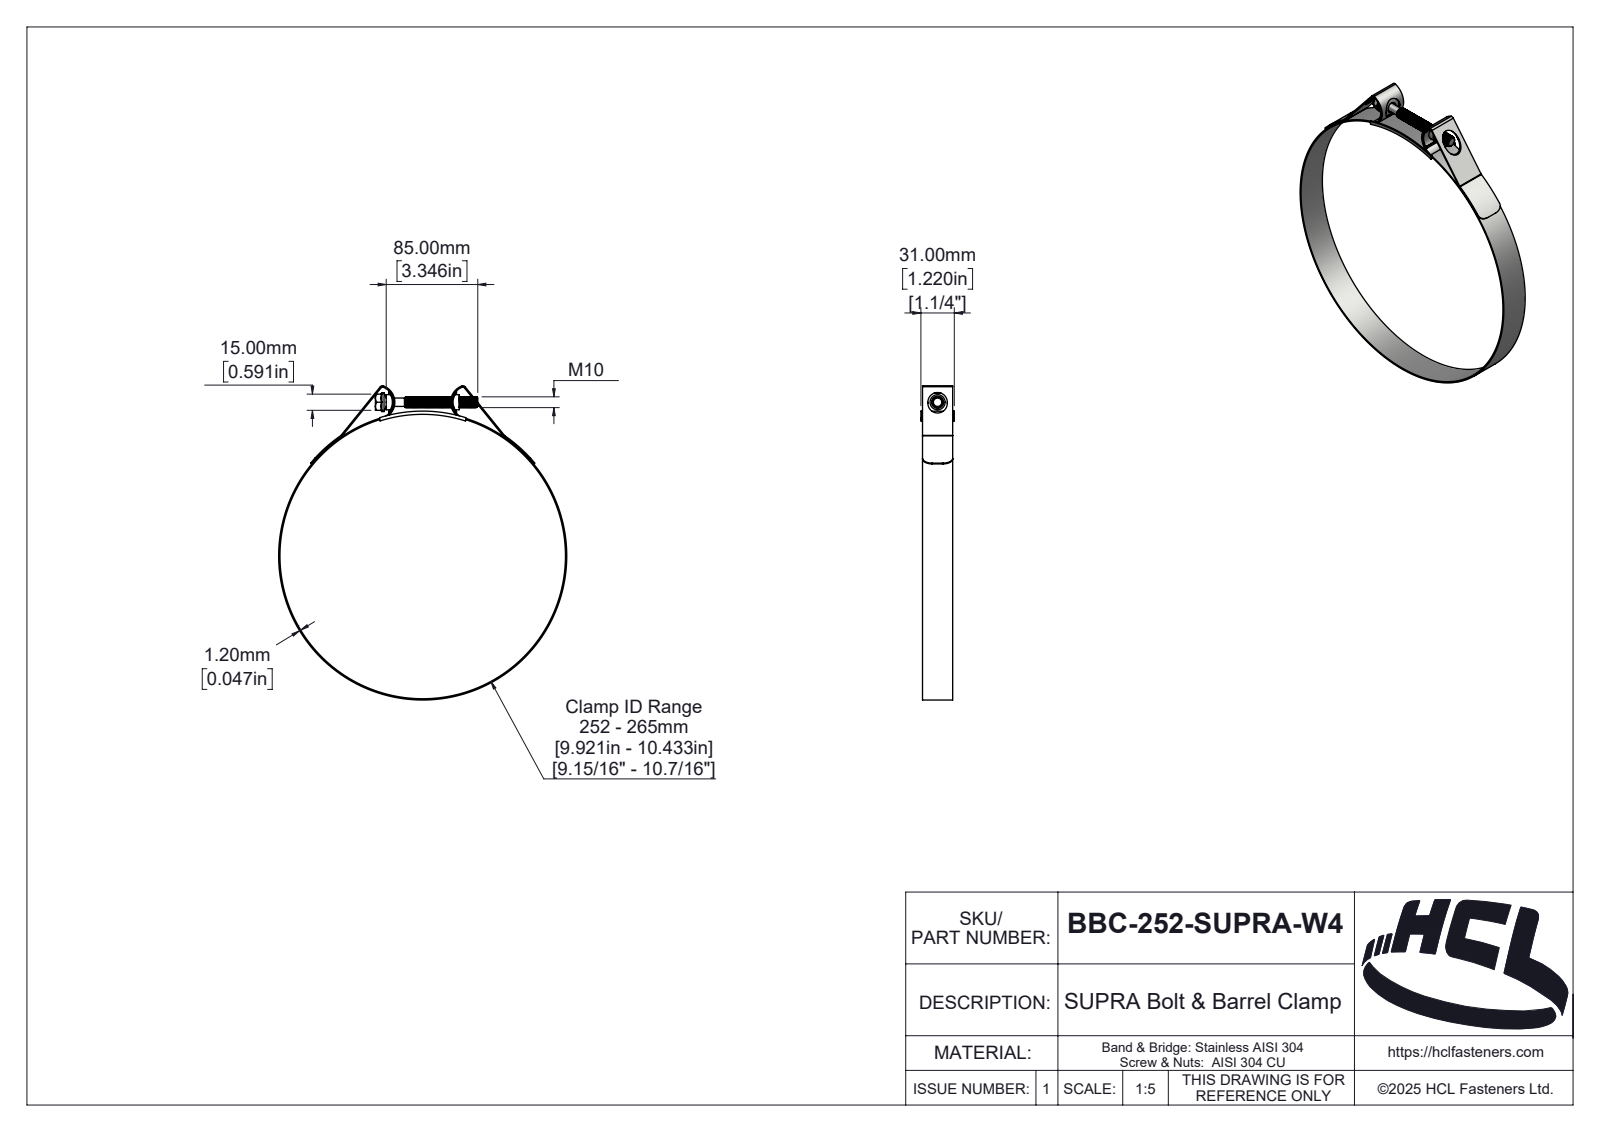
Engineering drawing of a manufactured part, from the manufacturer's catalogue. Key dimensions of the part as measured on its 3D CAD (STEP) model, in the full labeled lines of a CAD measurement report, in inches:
Part name (STEP PRODUCT): BBC-252-SUPRA-W4
STEP written by: SolidWorks 2025 (AUTOMOTIVE_DESIGN)
Units: inches
Bodies: 5 solids, 382 faces (50 planar, 245 cylindrical, 87 other)
Overall size (bounding box): 11.478 × 10.528 × 1.22
Volume: 2.8 in³ · Surface area: 111.2 in²
Round holes (diameter × count): ⌀10.433 ×1
Round bosses / shafts (diameter × count): ⌀10.528 ×1, ⌀0.682 ×1, ⌀0.551 ×1, ⌀0.394 ×1, ⌀0.307 ×1
Partial cylindrical surfaces — rounded edges, fillets, slot ends (radius × count): R0.039 ×4, R0.051 ×2, R0.079 ×2, R0.098 ×2, R0.126 ×2, R0.354 ×2, R0.543 ×2, R0.582 ×2
Main face-to-face distances: 0.047, 1.102, 0.059, 1.161, 1.173, 1.114, 1.22, 1.126, 0.591, 0.098
